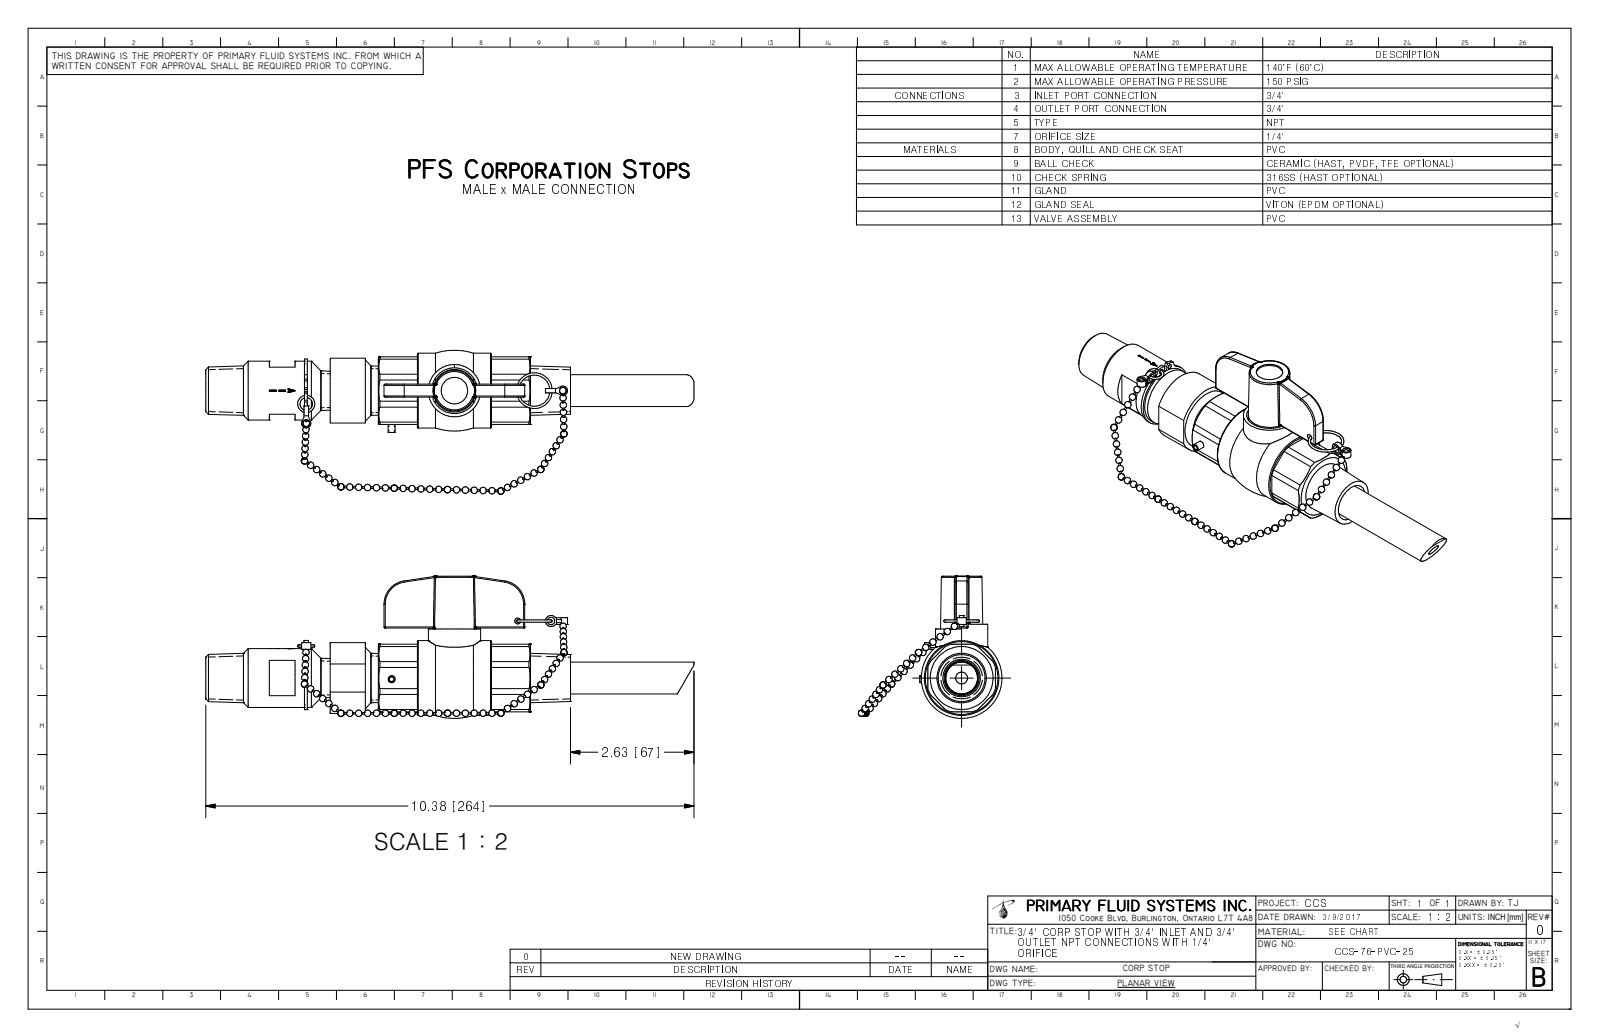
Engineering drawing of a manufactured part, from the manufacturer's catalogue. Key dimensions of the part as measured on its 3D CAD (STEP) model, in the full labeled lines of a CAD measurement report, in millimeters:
Part name (STEP PRODUCT): CCS-76-PVC-25_R0
STEP written by: Autodesk Inventor 2009 (AUTOMOTIVE_DESIGN)
Units: millimetres
Bodies: 1 solid, 380 faces (113 planar, 61 cylindrical, 206 other)
Overall size (bounding box): 263.7 × 77.5 × 76.6
Volume: 211 700 mm³ · Surface area: 44 000 mm²
Round holes (diameter × count): ⌀2.5 ×1, ⌀3.8 ×1, ⌀6.4 ×1, ⌀11.9 ×1, ⌀14.2 ×1, ⌀14.3 ×1, ⌀24.6 ×1
Round bosses / shafts (diameter × count): ⌀40.3 ×1, ⌀34.1 ×1, ⌀31.8 ×1, ⌀29 ×1, ⌀28.2 ×1, ⌀22.9 ×1, ⌀17.1 ×1, ⌀14.2 ×1
Partial cylindrical surfaces — rounded edges, fillets, slot ends (radius × count): R0.6 ×12, R1.4 ×2, R5 ×2, R12.7 ×2, R11.5 ×1, R14.3 ×1, R15.8 ×1, R19.1 ×1
Main face-to-face distances: 36.4, 14, 0.8, 7, 21, 4.7, 30.1, 9.2, 16.2, 5.5
Hole centre spacings: 17.5
